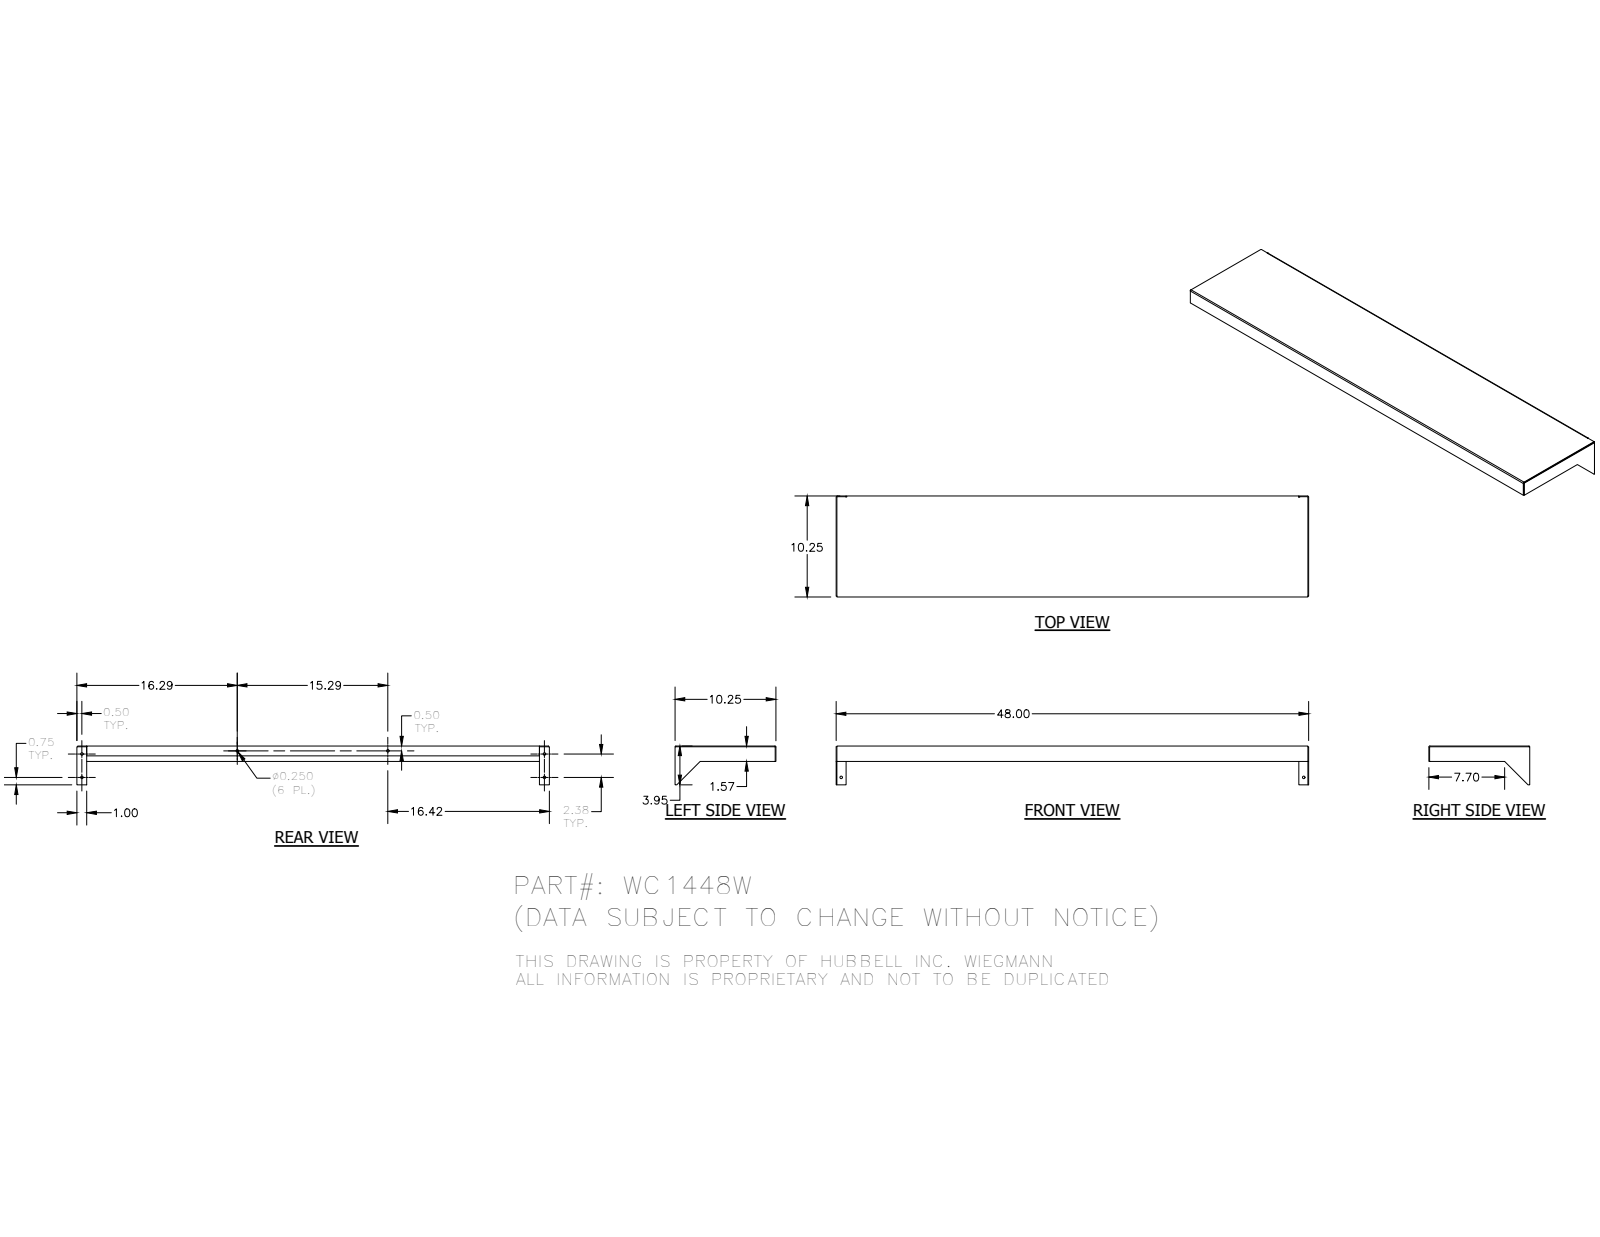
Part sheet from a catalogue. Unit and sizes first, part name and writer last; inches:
Units: inches
Overall size (bounding box): 48 × 10.25 × 3.949
Round holes (diameter × count): ⌀0.25 ×6
Partial cylindrical surfaces — rounded edges, fillets, slot ends (radius × count): R0.031 ×4, R0.105 ×4
Main face-to-face distances: 0.074, 10.176, 10.102, 10.25, 47.926, 47.852, 48, 1.574, 1.5, 1
Hole centre spacings: 2.375, 47, 47.06, 15.291, 15.796, 15.919, 16.022, 16.143
Volume: 47.78 in³ · Surface area: 1 305 in²
Bodies: 3 solids, 68 faces (54 planar, 14 cylindrical, 0 other)
Part name (STEP PRODUCT): WC1448WBKP; WC14WRS; WC14WLS; WC14W
STEP written by: Autodesk Inventor 2016 (AUTOMOTIVE_DESIGN)
